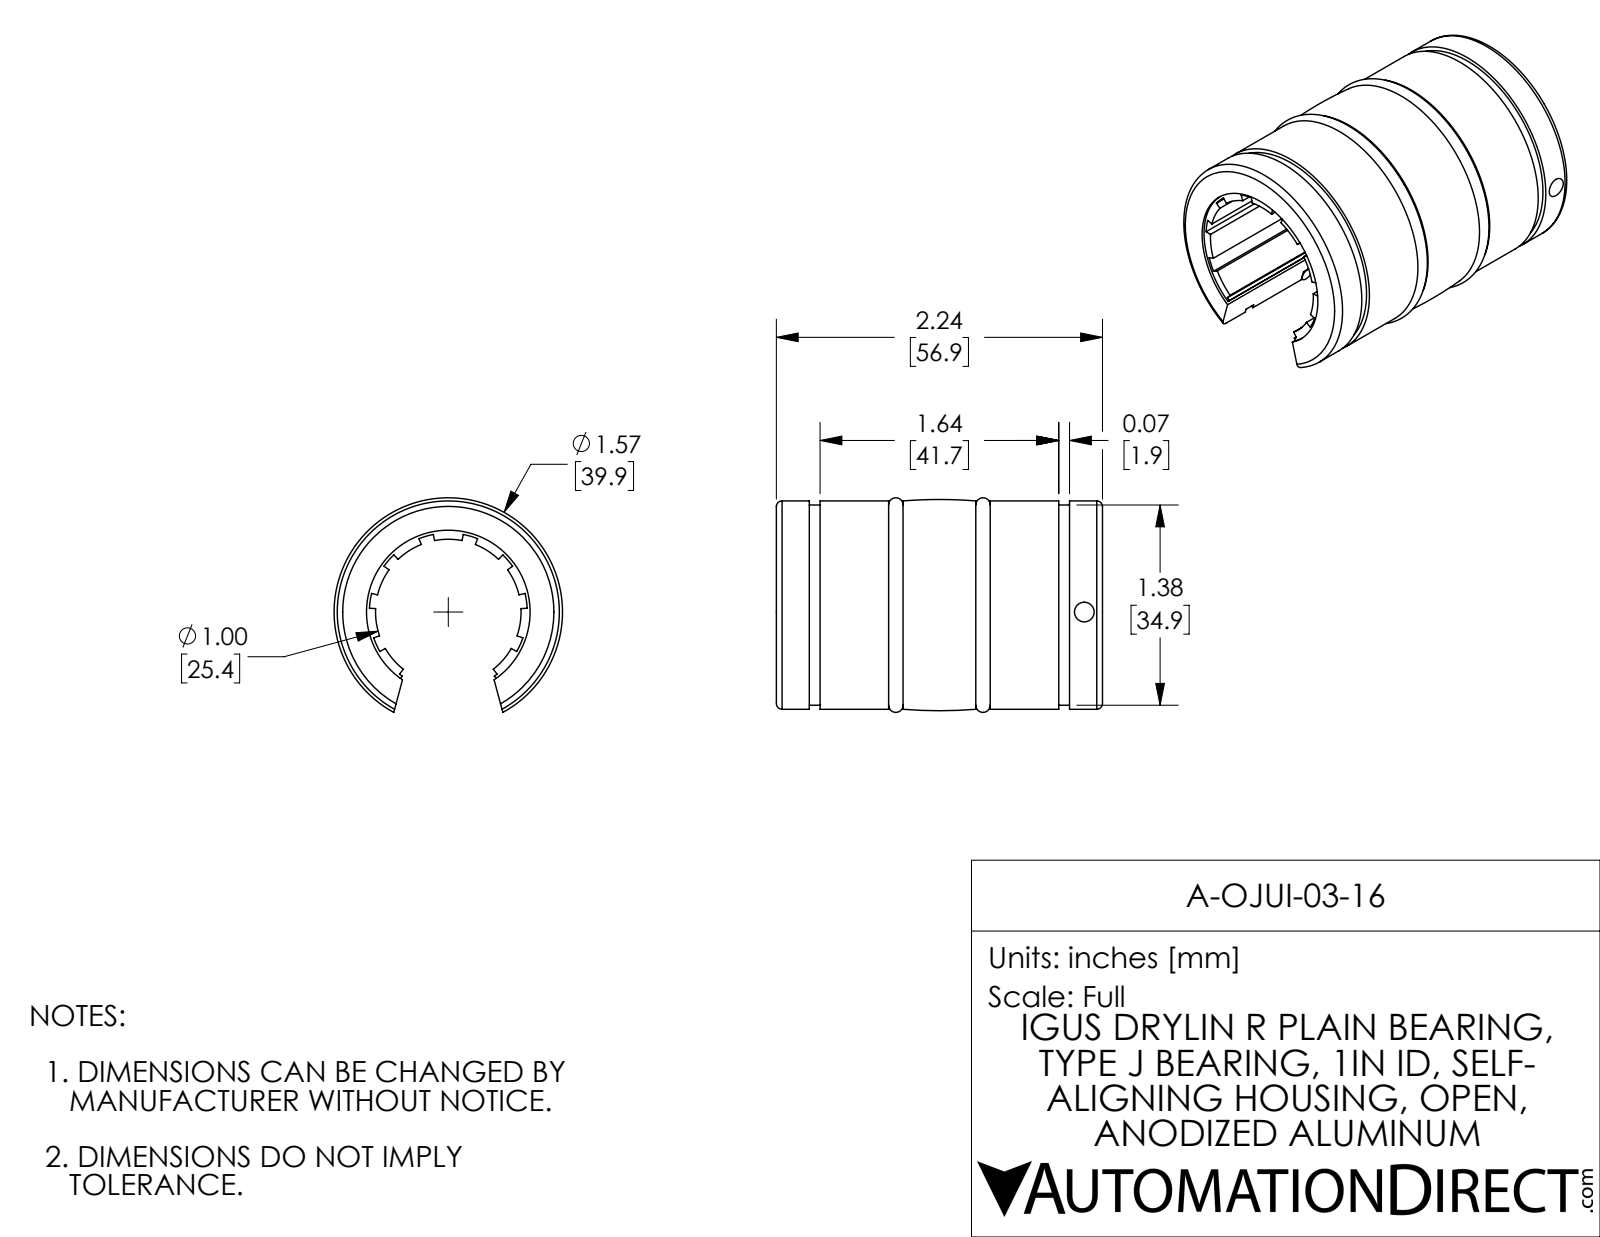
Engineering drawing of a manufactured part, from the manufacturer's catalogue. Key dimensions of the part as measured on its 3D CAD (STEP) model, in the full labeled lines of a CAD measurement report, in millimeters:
Part name (STEP PRODUCT): A-OJUI-03-16
STEP written by: SolidWorks 2017 (AUTOMOTIVE_DESIGN)
Units: millimetres
Bodies: 4 solids, 142 faces (77 planar, 44 cylindrical, 21 other)
Overall size (bounding box): 56.9 × 39.9 × 37.5
Volume: 29 940 mm³ · Surface area: 23 330 mm²
Round holes (diameter × count): ⌀3.5 ×1, ⌀28.6 ×1, ⌀30.6 ×1
Round bosses / shafts (diameter × count): ⌀38.8 ×1, ⌀37.4 ×1, ⌀34.8 ×1, ⌀3.8 ×1
Partial cylindrical surfaces — rounded edges, fillets, slot ends (radius × count): R12.7 ×1, R13.8 ×1, R15.1 ×1
Main face-to-face distances: 19.6, 37.3, 22.1, 34.8, 2.5, 15.2, 56.9, 26.1, 30.9, 6.5
